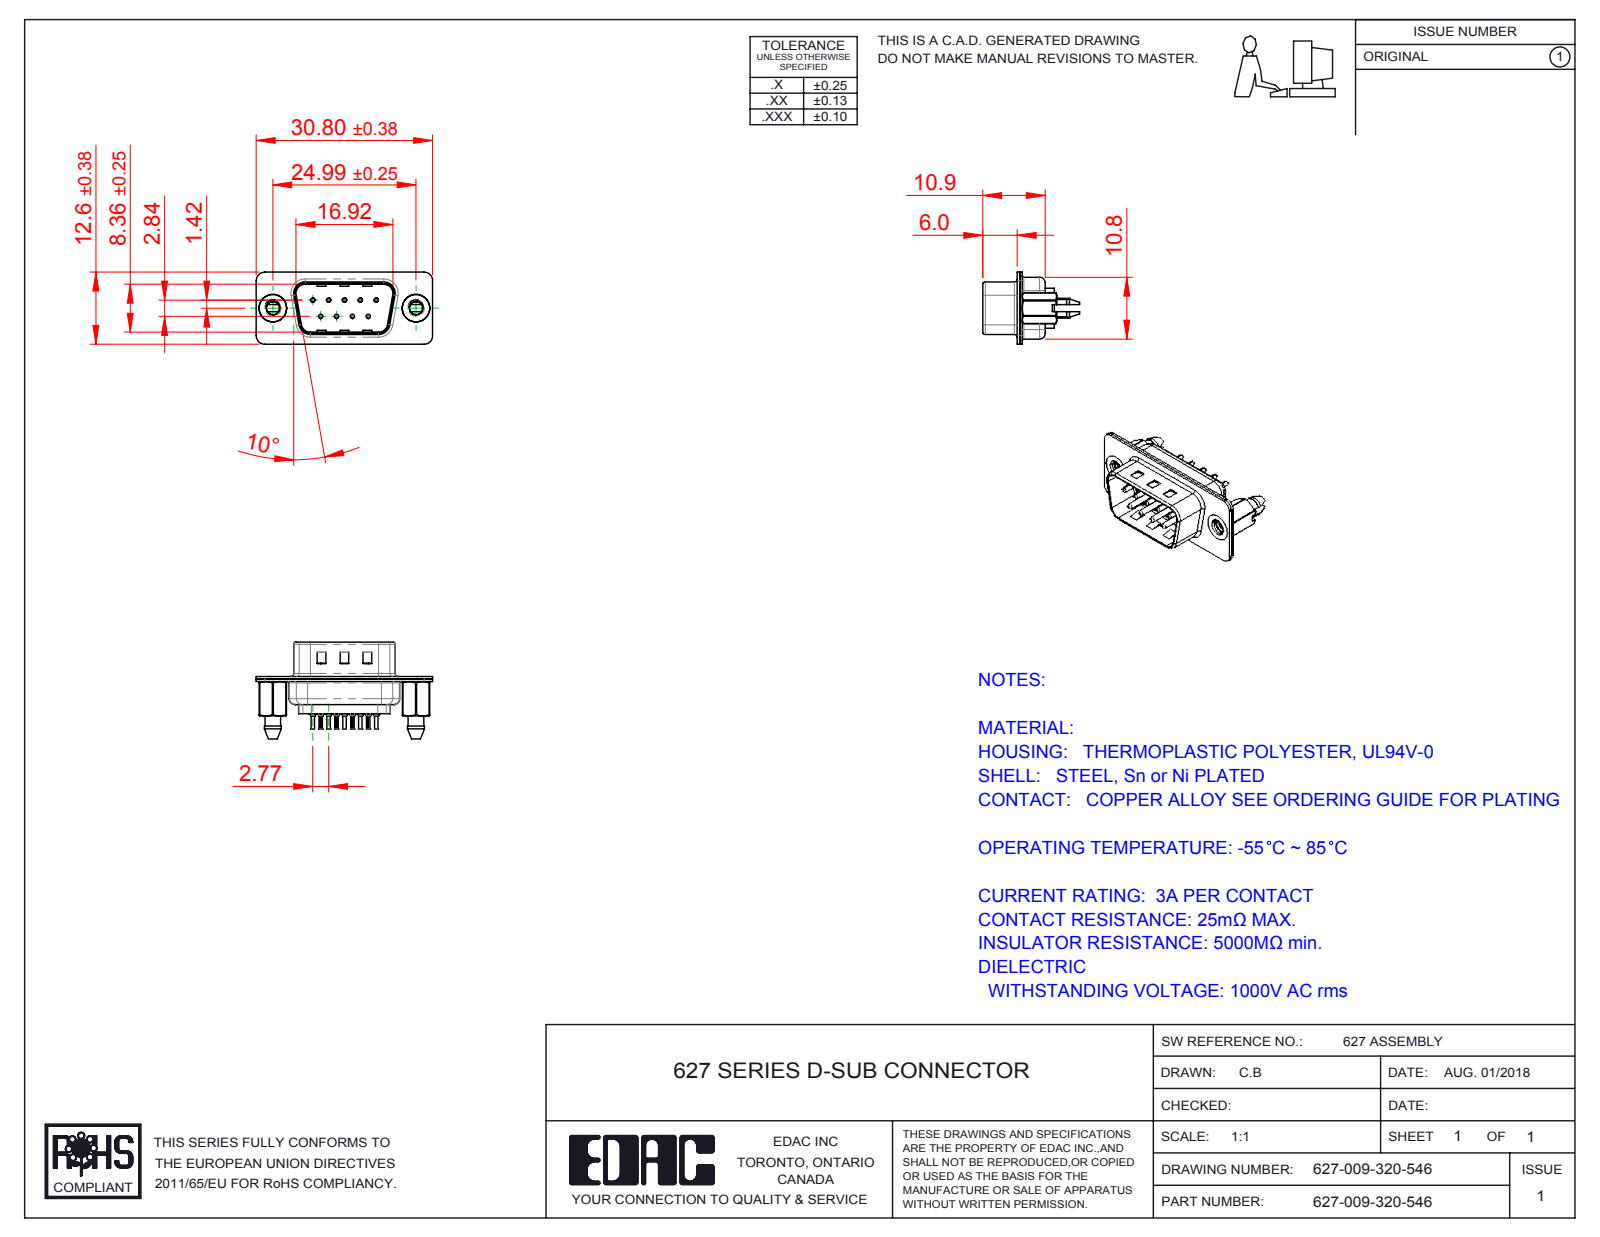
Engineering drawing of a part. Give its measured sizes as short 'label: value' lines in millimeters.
name: 627 Housing_09 LP; 627 Shell Front_09 Contacts; 627 Contact Row 2_20L; 627 4-40 Threaded Boardlock_LP (+3 more)
written by: SolidWorks 2016 (CONFIG_CONTROL_DESIGN)
unit: mm
bodies: 14 solids, 1260 faces (355 planar, 494 cylindrical, 411 other)
size: 30.8 × 16.9 × 12.6
volume: 1 422 mm³; area: 4 171 mm²
holes: 9× ⌀0.2, 9× ⌀0.35, 9× ⌀1.1, 9× ⌀1.6, 2× ⌀2.26, 2× ⌀4, 2× ⌀4.8
bosses: 9× ⌀2, 9× ⌀1.5, 9× ⌀0.75, 9× ⌀0.6, 2× ⌀4.9
rounds: 20× R1.5, 18× R0.1, 12× R2, 10× R1.6, 8× R0.5, 4× R0.25, 4× R0.6, 4× R0.65
face distances: 0.45, 0.4, 0.9, 0.82, 9.58, 1.4, 8.76, 6.5, 0.5, 1.5
hole spacings: 3.16, 2.77, 5.54, 5.03, 5.04, 8.31, 7.48, 7.49
